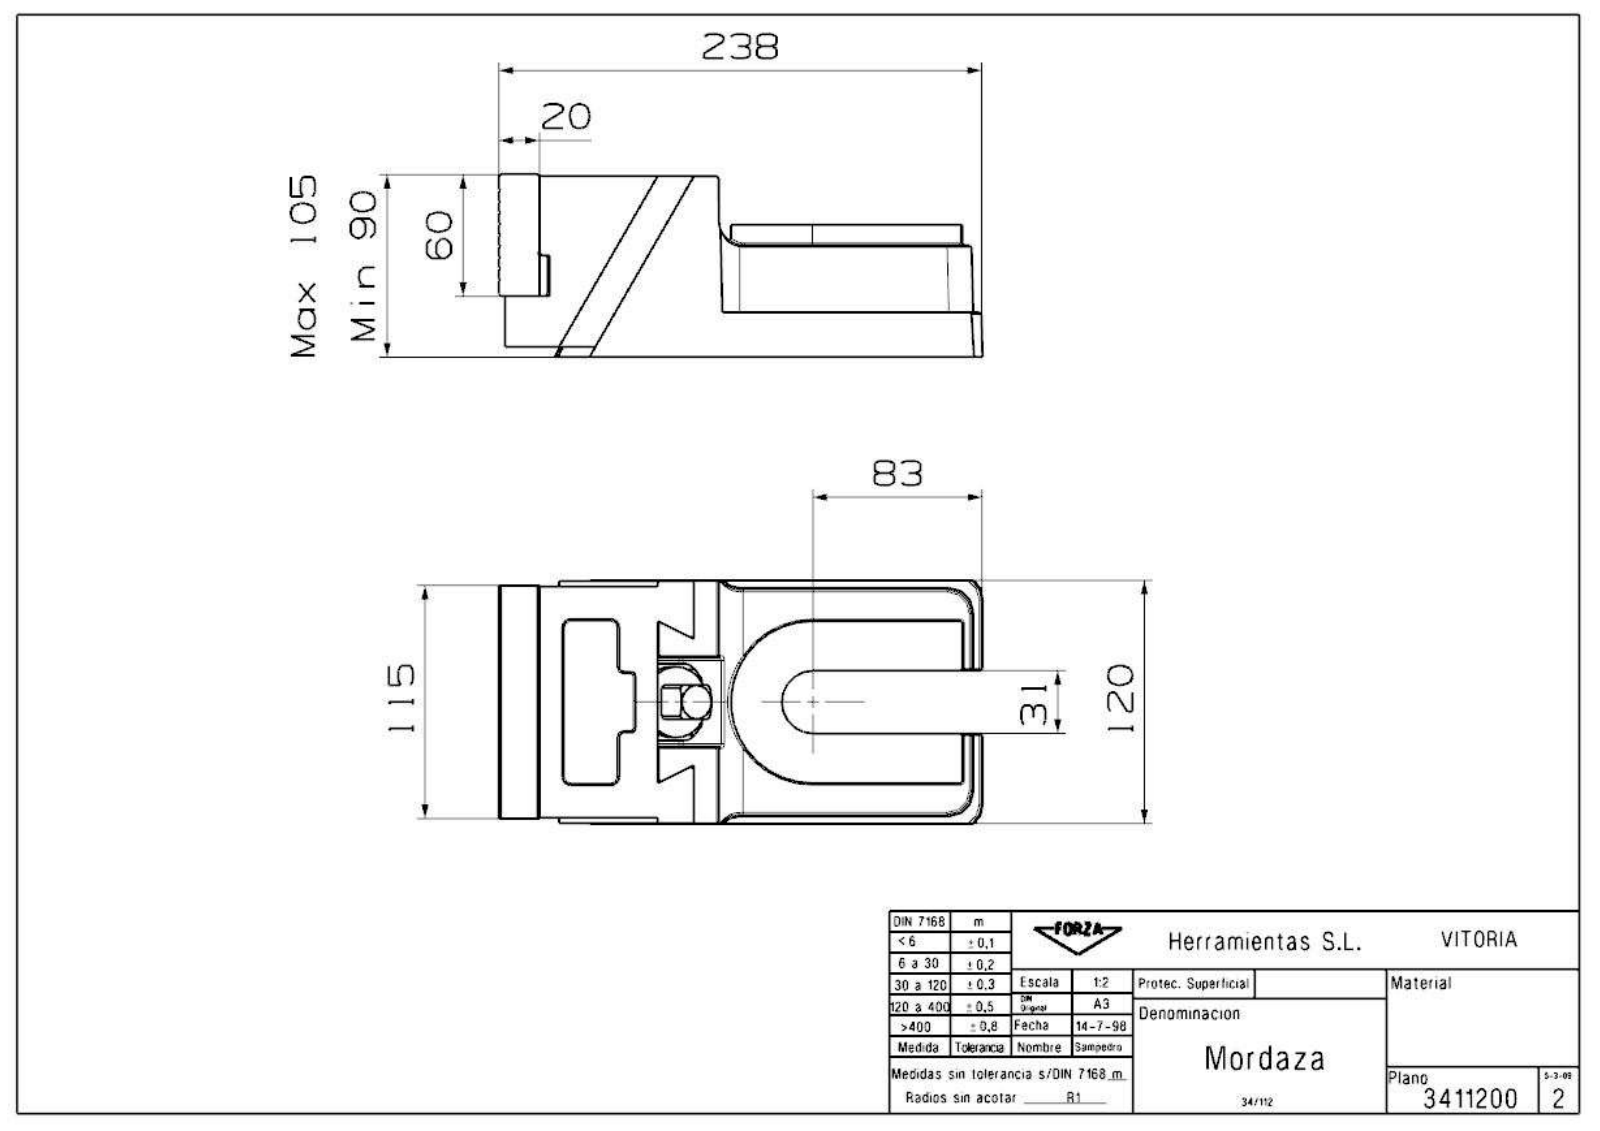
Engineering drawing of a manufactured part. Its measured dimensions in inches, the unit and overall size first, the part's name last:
Units: inches
Overall size (bounding box): 9.378 × 4.768 × 3.543
Round holes (diameter × count): ⌀0.079 ×2, ⌀0.406 ×2, ⌀0.512 ×2, ⌀0.787 ×2, ⌀0.679 ×1, ⌀0.709 ×1, ⌀0.913 ×1, ⌀1.004 ×1
Round bosses / shafts (diameter × count): ⌀0.984 ×2, ⌀1.378 ×1, ⌀1.124 ×1, ⌀0.937 ×1, ⌀0.866 ×1, ⌀0.701 ×1
Partial cylindrical surfaces — rounded edges, fillets, slot ends (radius × count): R0.039 ×36, R0.157 ×12, R0.059 ×7, R0.472 ×7, R0.079 ×6, R0.354 ×6, R0.433 ×1, R0.61 ×1
Main face-to-face distances: 0.945, 1.378, 2.323, 0.984, 1.752, 2.972, 0.118, 0.787, 0.61, 1.634
Hole centre spacings: 0.157, 0.236, 0.554, 0.554, 2.953, 2.957
Volume: 101.1 in³ · Surface area: 310.3 in²
Bodies: 6 solids, 356 faces (189 planar, 109 cylindrical, 58 other)
Part name (STEP PRODUCT): 3411200_Mordaza
STEP written by: SIEMENS PLM Software NX 9.0 (CONFIG_CONTROL_DESIGN)
